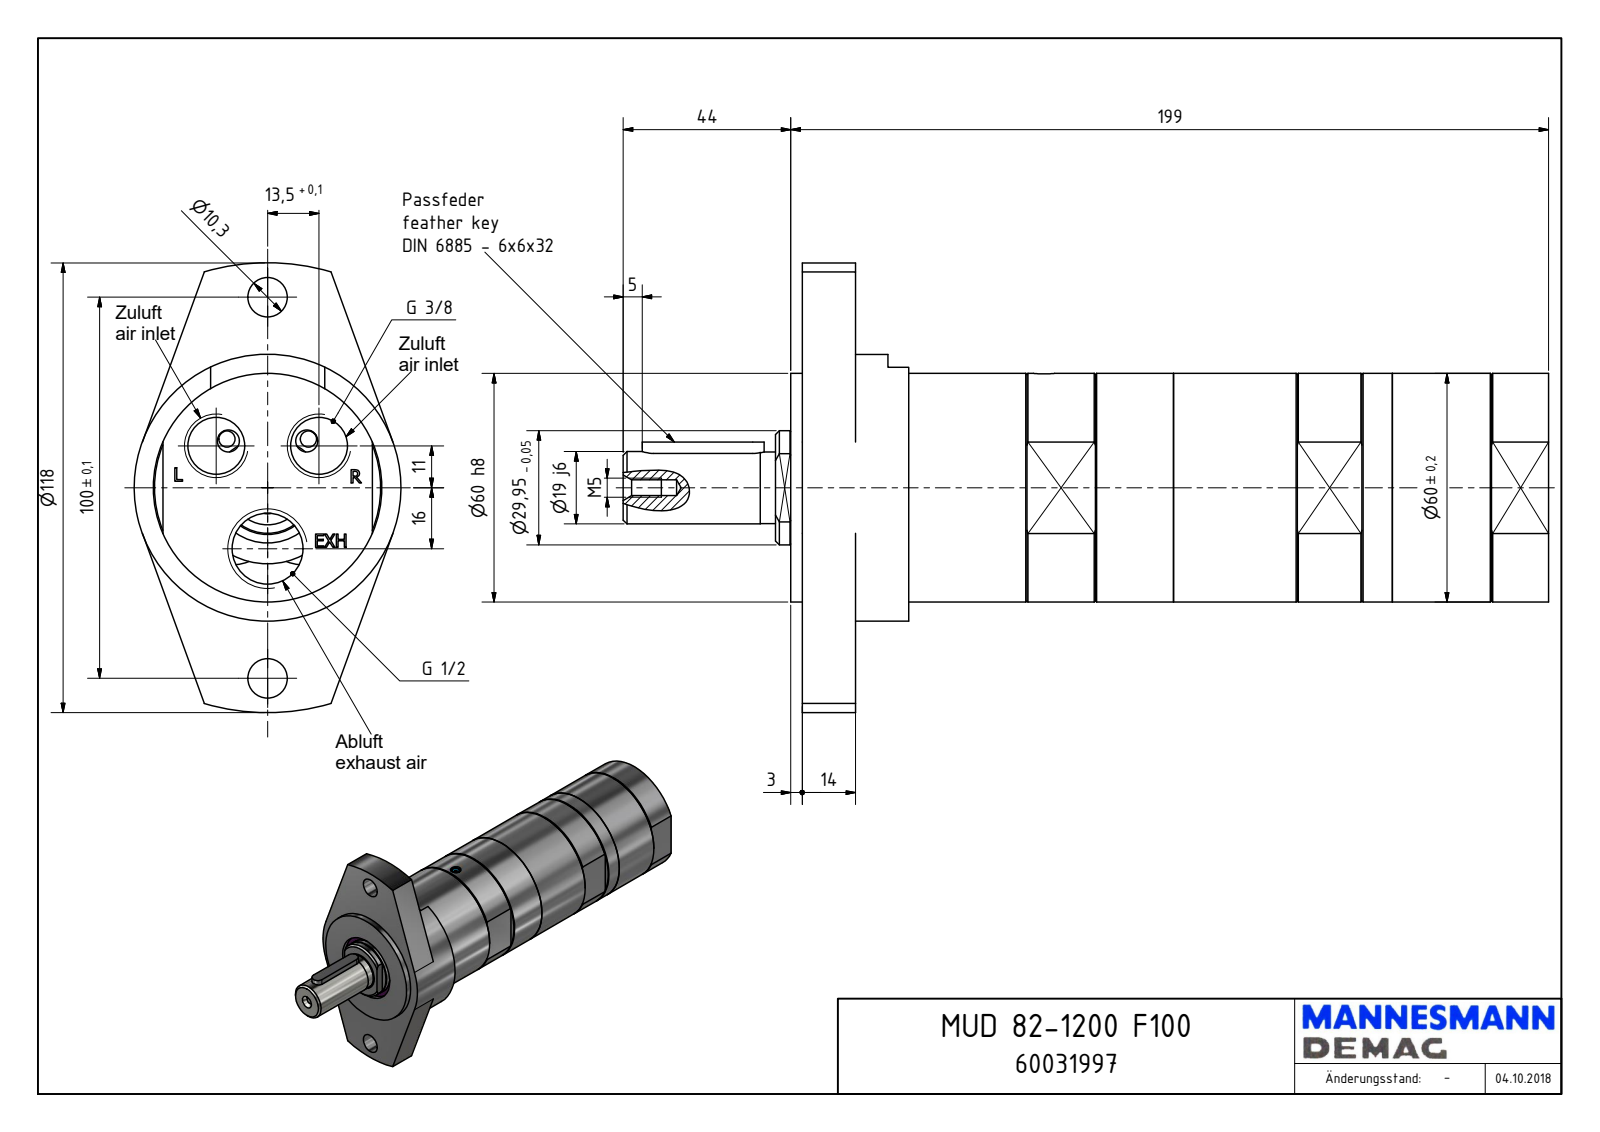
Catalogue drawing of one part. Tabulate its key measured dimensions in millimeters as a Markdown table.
| quantity | value |
| --- | --- |
| part name | MUD 82-1200 F100_60031997 |
| STEP written by | Autodesk Inventor 2018 (AUTOMOTIVE_DESIGN) |
| units | millimeters |
| bodies | 1 solid, 201 faces (115 planar, 47 cylindrical, 39 other) |
| overall size | 243 × 118 × 70 |
| volume | 616 563 mm³ |
| surface area | 62 037 mm² |
| round holes (diameter × count) | 10.3 × 2, 14.95 × 2, 1.55 × 1, 4 × 1, 4.13 × 1, 5.5 × 1, 18.63 × 1, 35 × 1 |
| round bosses / shafts (diameter × count) | 70 × 1, 60 × 1, 55.18 × 1, 29.95 × 1, 19 × 1, 18.8 × 1, 5 × 1, 3.6 × 1 |
| partial cylindrical surfaces (radius × count) | 3 × 2, 7.5 × 2, 8.5 × 1, 19.5 × 1, 23.5 × 1, 26.19 × 1, 59 × 1 |
| main face-to-face distances | 14, 17, 3, 196, 182, 199, 55, 31, 28, 168 |
| hole center spacings | 17.41, 30.19, 41.27, 50, 62.48, 16, 27, 34 |
